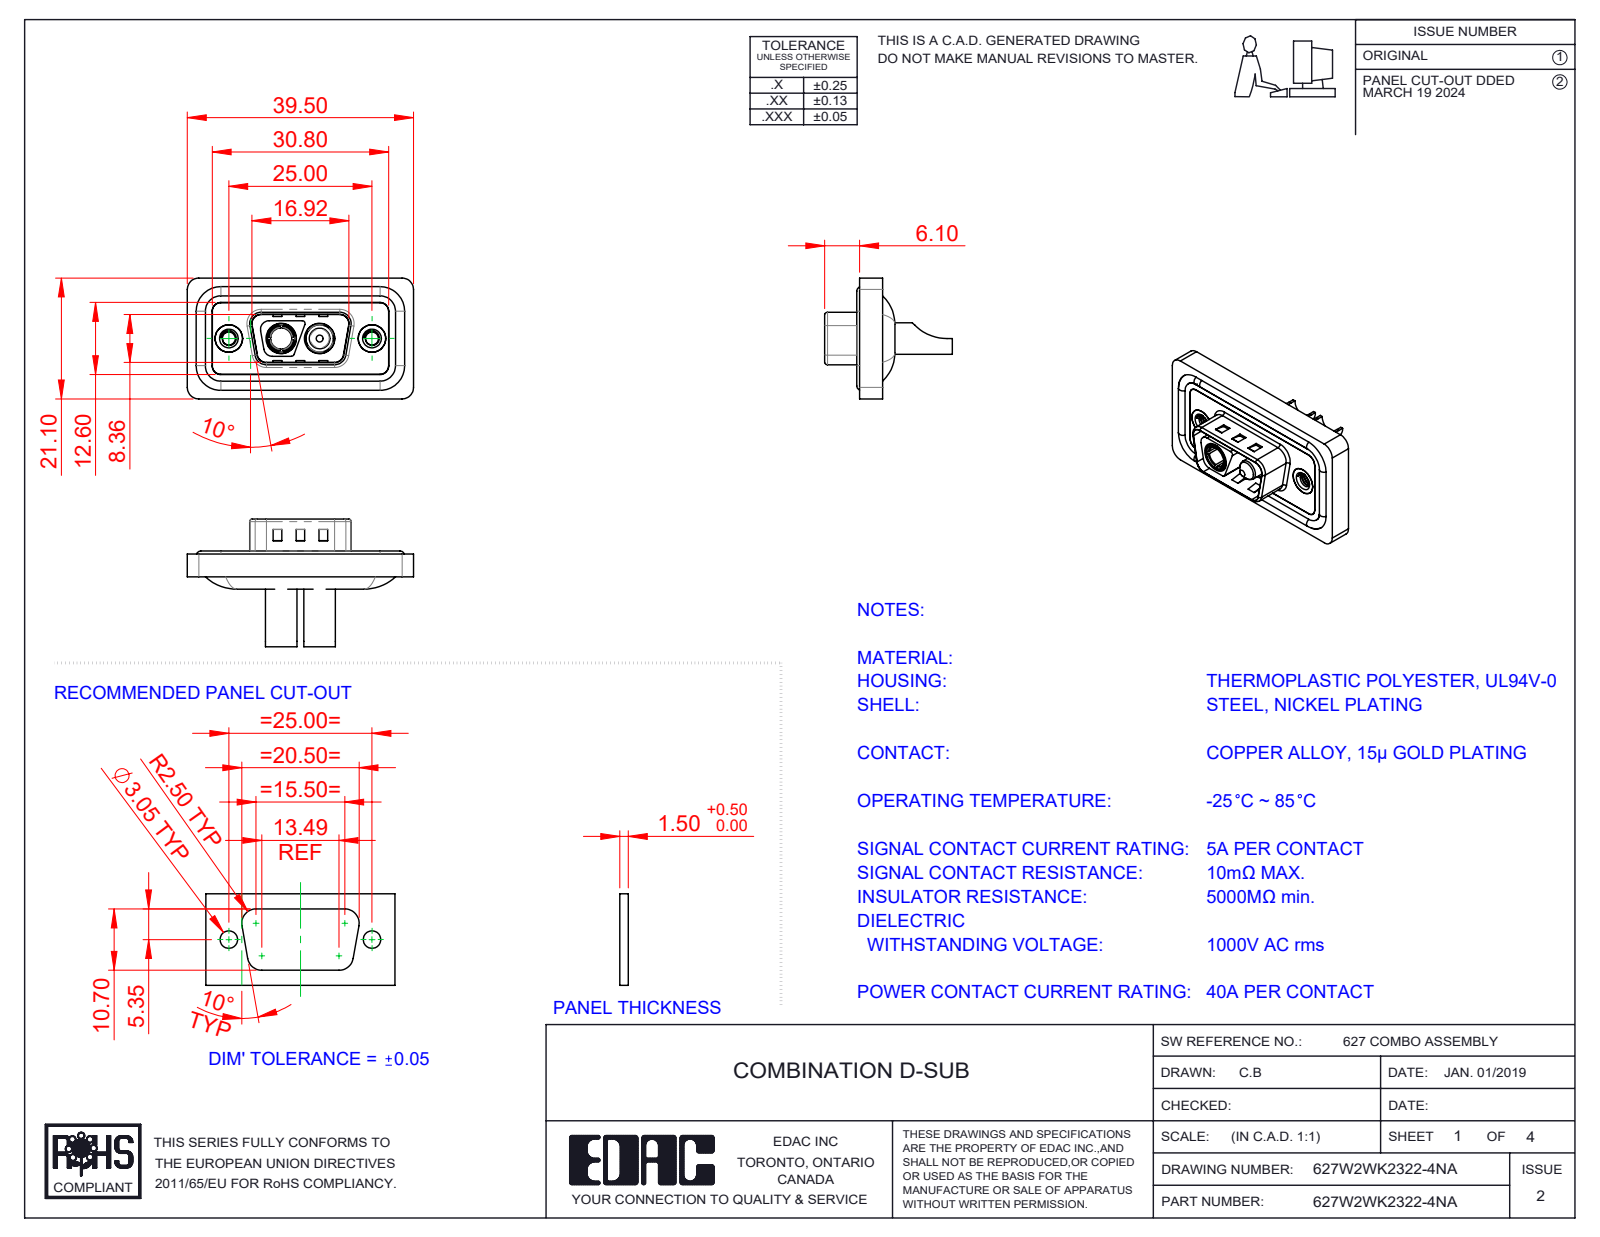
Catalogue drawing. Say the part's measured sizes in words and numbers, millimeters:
The part is named "627Combo Housing_2WK2; Power Socket_40A SC; 627Combo Threaded Rivet_A; 627Combo Shell Front_09 Contacts (+4 more)". Its 3-D file was written by "SolidWorks 2023 (CONFIG_CONTROL_DESIGN)". It is 11 solids with 540 faces: 193 planar, 231 cylindrical and 116 other. Overall it measures 39.5 by 22.3 by 21.1 millimeters. Its volume is 4 636 cubic millimeters and its surface area 7 620 square millimeters. Round holes: 2 of diameter 2.26, 2 of diameter 4, 2 of diameter 4.6, 2 of diameter 4.8, 2 of diameter 4.85, 2 of diameter 5, 2 of diameter 5.3, 1 of diameter 3.7. Round bosses or shafts: 4 of diameter 1.6, 2 of diameter 5.5, 2 of diameter 5.2, 2 of diameter 4.9, 2 of diameter 4.75, 2 of diameter 3.75, 1 of diameter 4.96, 1 of diameter 3.6. Partial cylindrical surfaces (rounded edges, fillets, slot ends): 24 of radius 1.5, 18 of radius 2, 10 of radius 0.5, 8 of radius 1.6, 4 of radius 0.25, 4 of radius 0.6, 4 of radius 0.65, 4 of radius 0.9. The main face-to-face distances are 0.4, 1.1, 2.9, 0.5, 3.1, 1.6, 2.5, 1.8, 3.2, 1.5. The hole center spacings are 9.14, 15.86, 6.72, 25.
